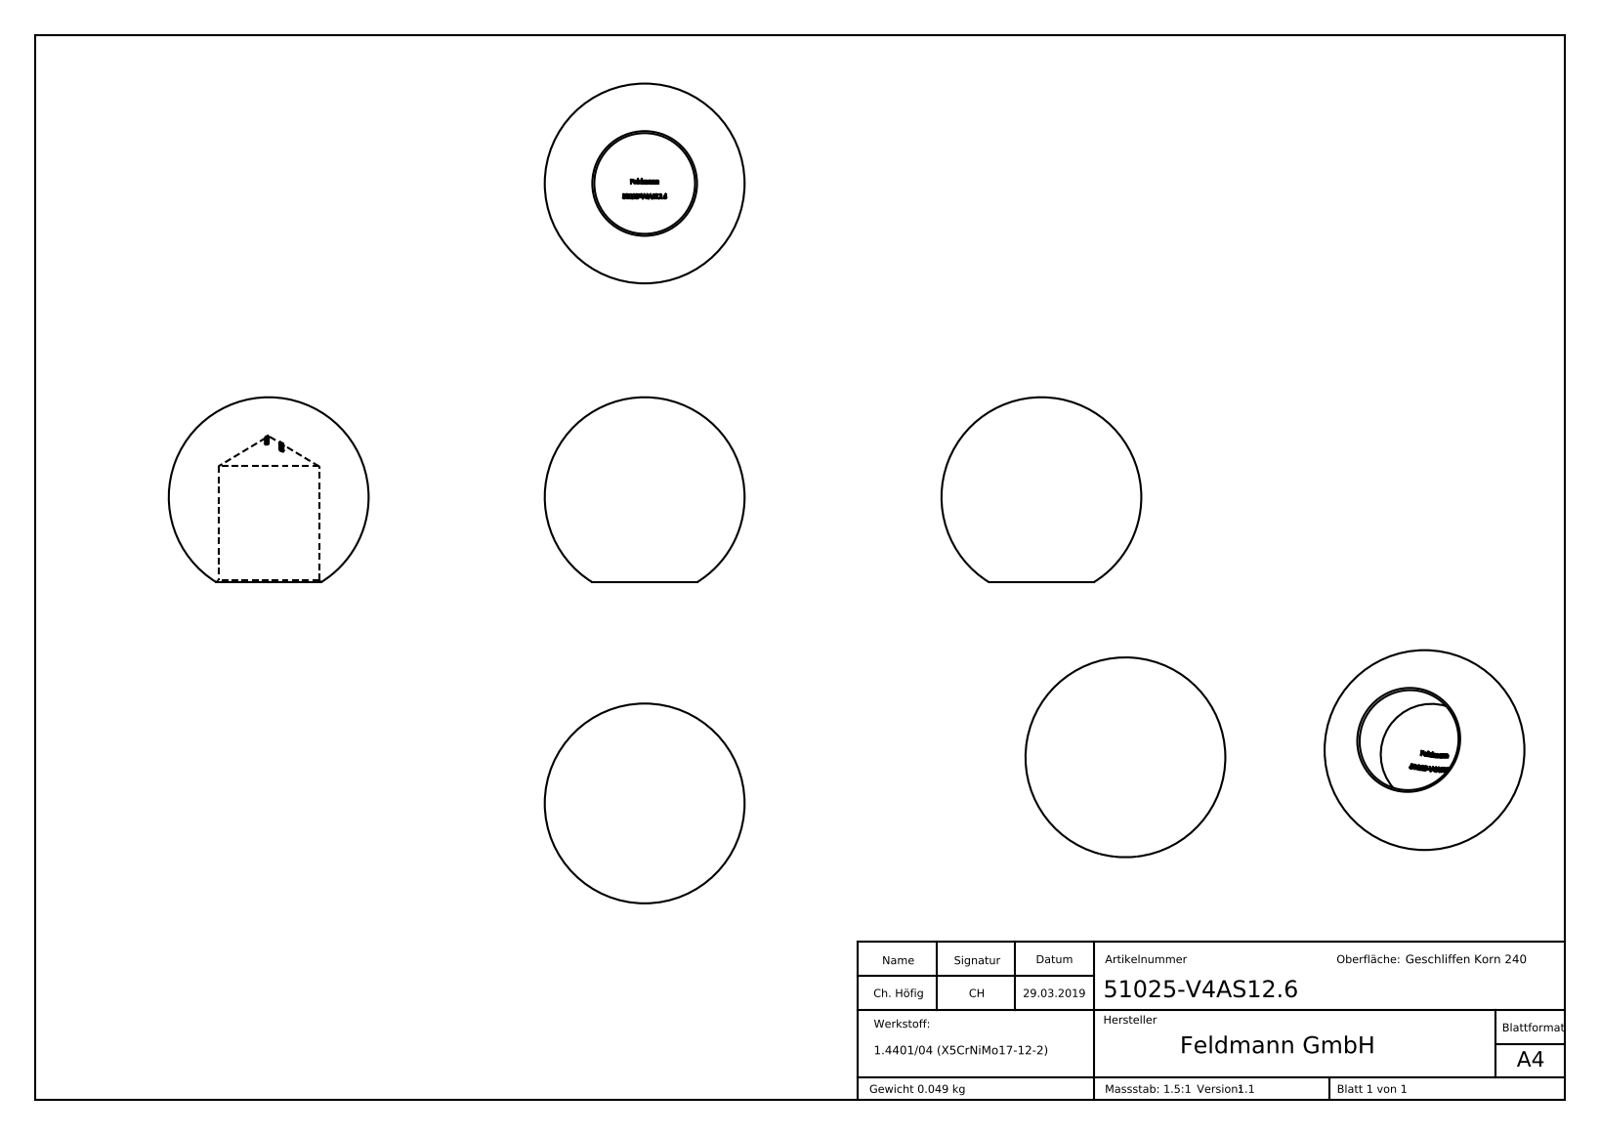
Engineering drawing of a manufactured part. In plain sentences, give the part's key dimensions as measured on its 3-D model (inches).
The part is named "51025-V4AS12.6". Its 3-D file was written by "SolidWorks 2015 (CONFIG_CONTROL_DESIGN)". It is 1 solid with 287 faces: 130 planar, 2 cylindrical and 155 other. Overall it measures 0.984 by 0.984 by 0.911 inches. Its volume is 0.371 cubic inches and its surface area 3.948 square inches. Round holes: 1 of diameter 0.496. The main face-to-face distances are 0.076, 0.072, 0.074, 0.05, 0.021, 0.098, 0.022, 0.053, 0.047, 0.026.
